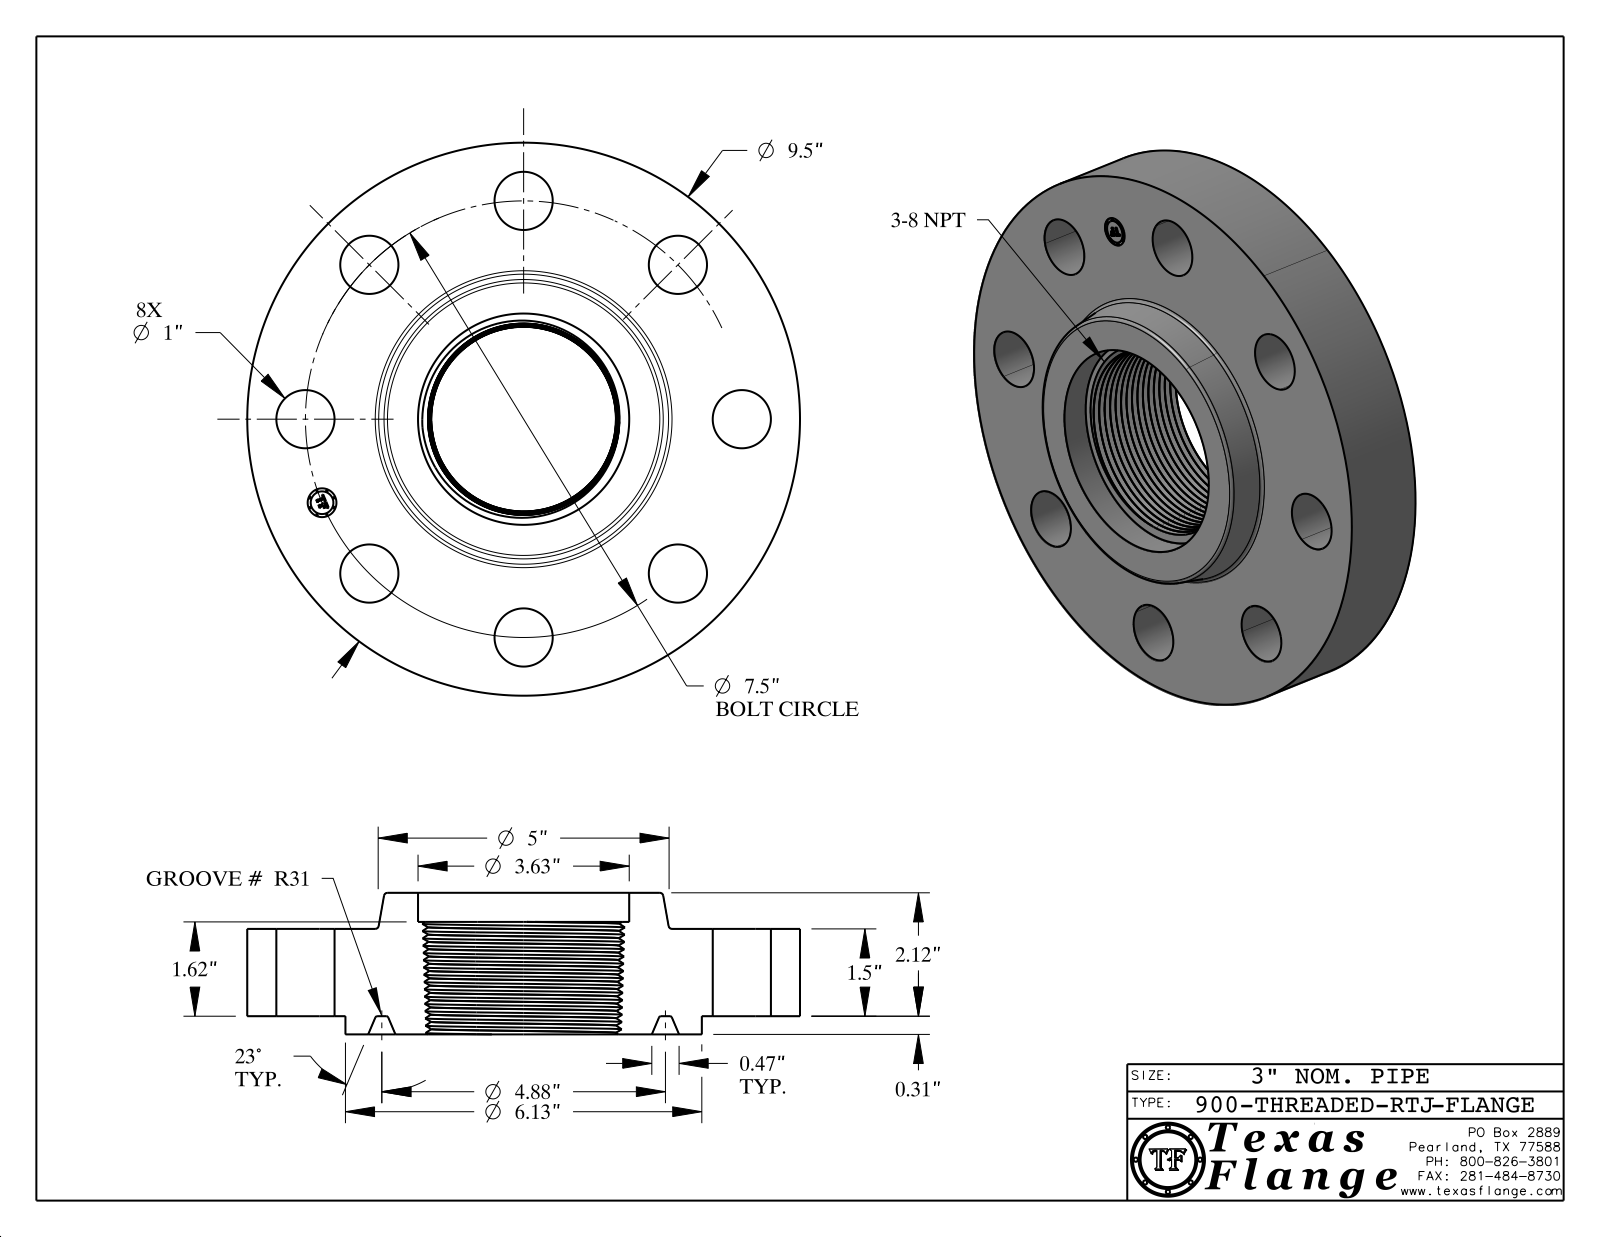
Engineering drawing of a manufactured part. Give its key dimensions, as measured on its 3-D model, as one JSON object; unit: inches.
{"part_name": "900-THREADED-RTJ", "step_written_by": "CATIA V5 STEP AP214 (AUTOMOTIVE_DESIGN)", "units": "inches", "bodies": {"solids": 1, "faces": 589, "planar": 372, "cylindrical": 42, "other": 175}, "overall_size": [9.5, 9.5, 2.433], "volume_in3": 94.16, "surface_area_in2": 257.6, "round_holes": [[1, 8], [0.495, 1], [3.63, 1]], "round_bosses_or_shafts": [[0.03, 8], [9.5, 1], [6.125, 1], [0.39, 1]], "face_to_face_distances": [1.5, 0.313, 1.813, 2.433, 2.12, 0.62, 1.933, 1.62, 0.12, 0.5], "hole_center_spacings": [3.75, 2.87, 5.303, 6.929, 1.463, 6.236, 7.356, 7.5]}
